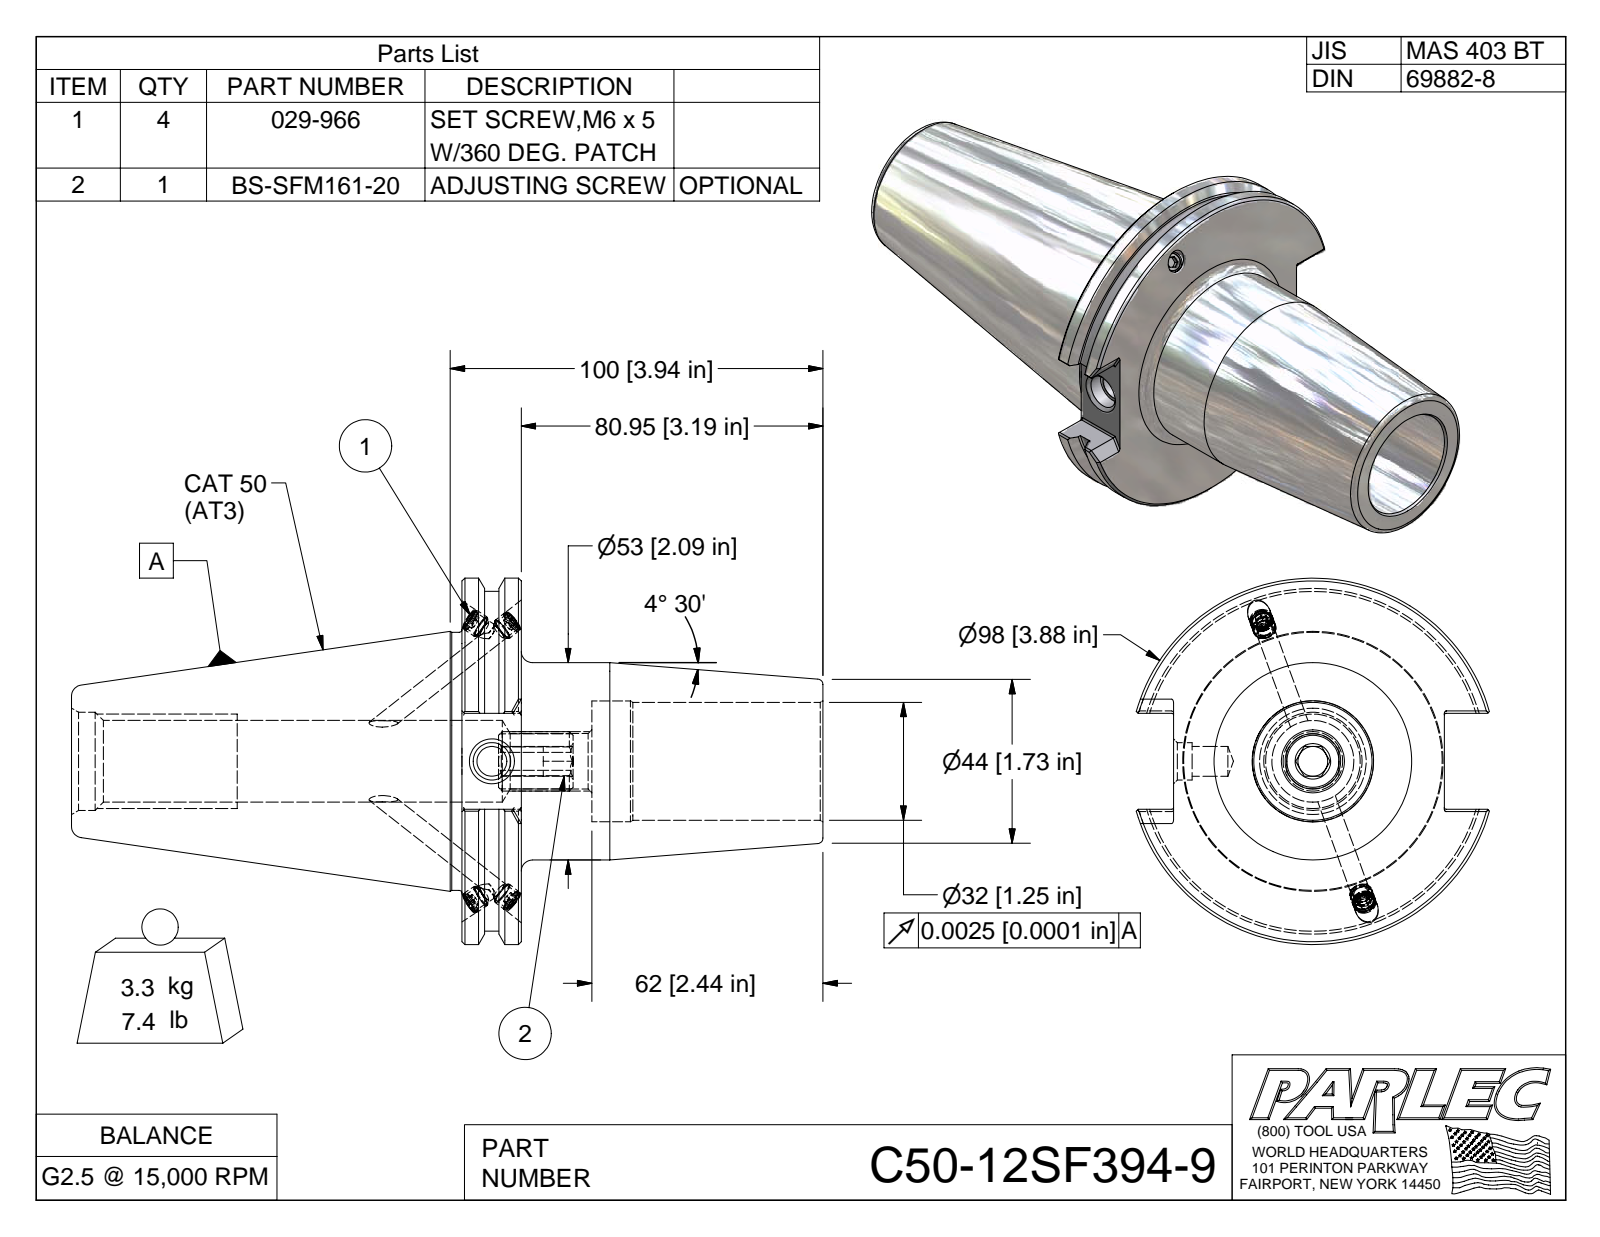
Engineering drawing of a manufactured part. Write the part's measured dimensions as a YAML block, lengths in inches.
part_name: "C50-12SF394-9; C50BC-12SF394-9-1; BS-SFM161-20; 029-966"
step_written_by: "Autodesk Inventor 2009 (AUTOMOTIVE_DESIGN)"
units: inches
bodies: {solids: 6, faces: 184, planar: 87, cylindrical: 44, other: 53}
overall_size: [7.937, 3.875, 3.729]
volume: 25.94
surface_area: 103.7
round_holes:
  - {diameter: 0.197, count: 4}
  - {diameter: 0.24, count: 4}
  - {diameter: 1.248, count: 1}
  - {diameter: 1.278, count: 1}
round_bosses_or_shafts:
  - {diameter: 0.244, count: 4}
  - {diameter: 0.236, count: 4}
  - {diameter: 3.875, count: 1}
  - {diameter: 3.594, count: 1}
  - {diameter: 2.73, count: 1}
  - {diameter: 2.087, count: 1}
partial_cylinders:
  - {radius: 0.02, count: 12}
  - {radius: 0.315, count: 1}
face_to_face_distances: [0.625, 1.371, 0.746, 3.812, 3.187, 2.441, 4.125, 4.75, 5.496, 7.937]
